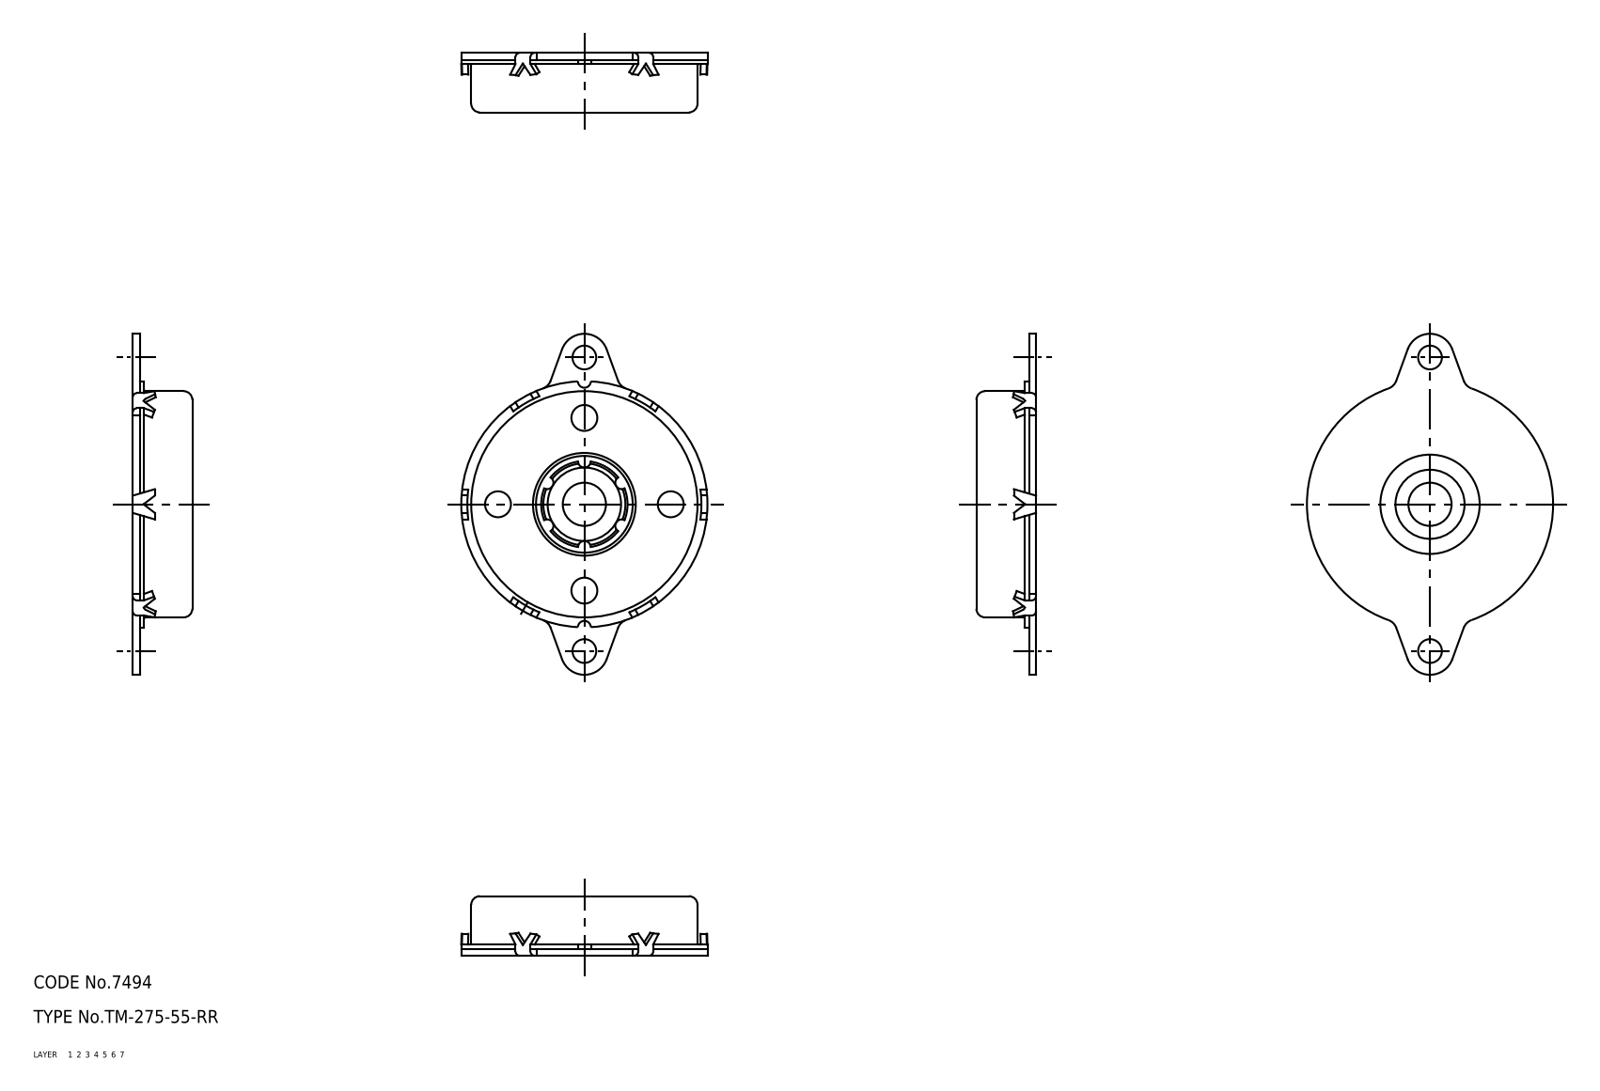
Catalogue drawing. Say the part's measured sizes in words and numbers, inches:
The part is named "67119995; 67120008". Its 3-D file was written by "CADfix (AUTOMOTIVE_DESIGN)". It is 2 solids with 216 faces: 0 planar, 0 cylindrical and 216 other. Overall it measures 3.11 by 2.244 by 0.543 inches. Its volume is 1.761 cubic inches and its surface area 16.7 square inches.
